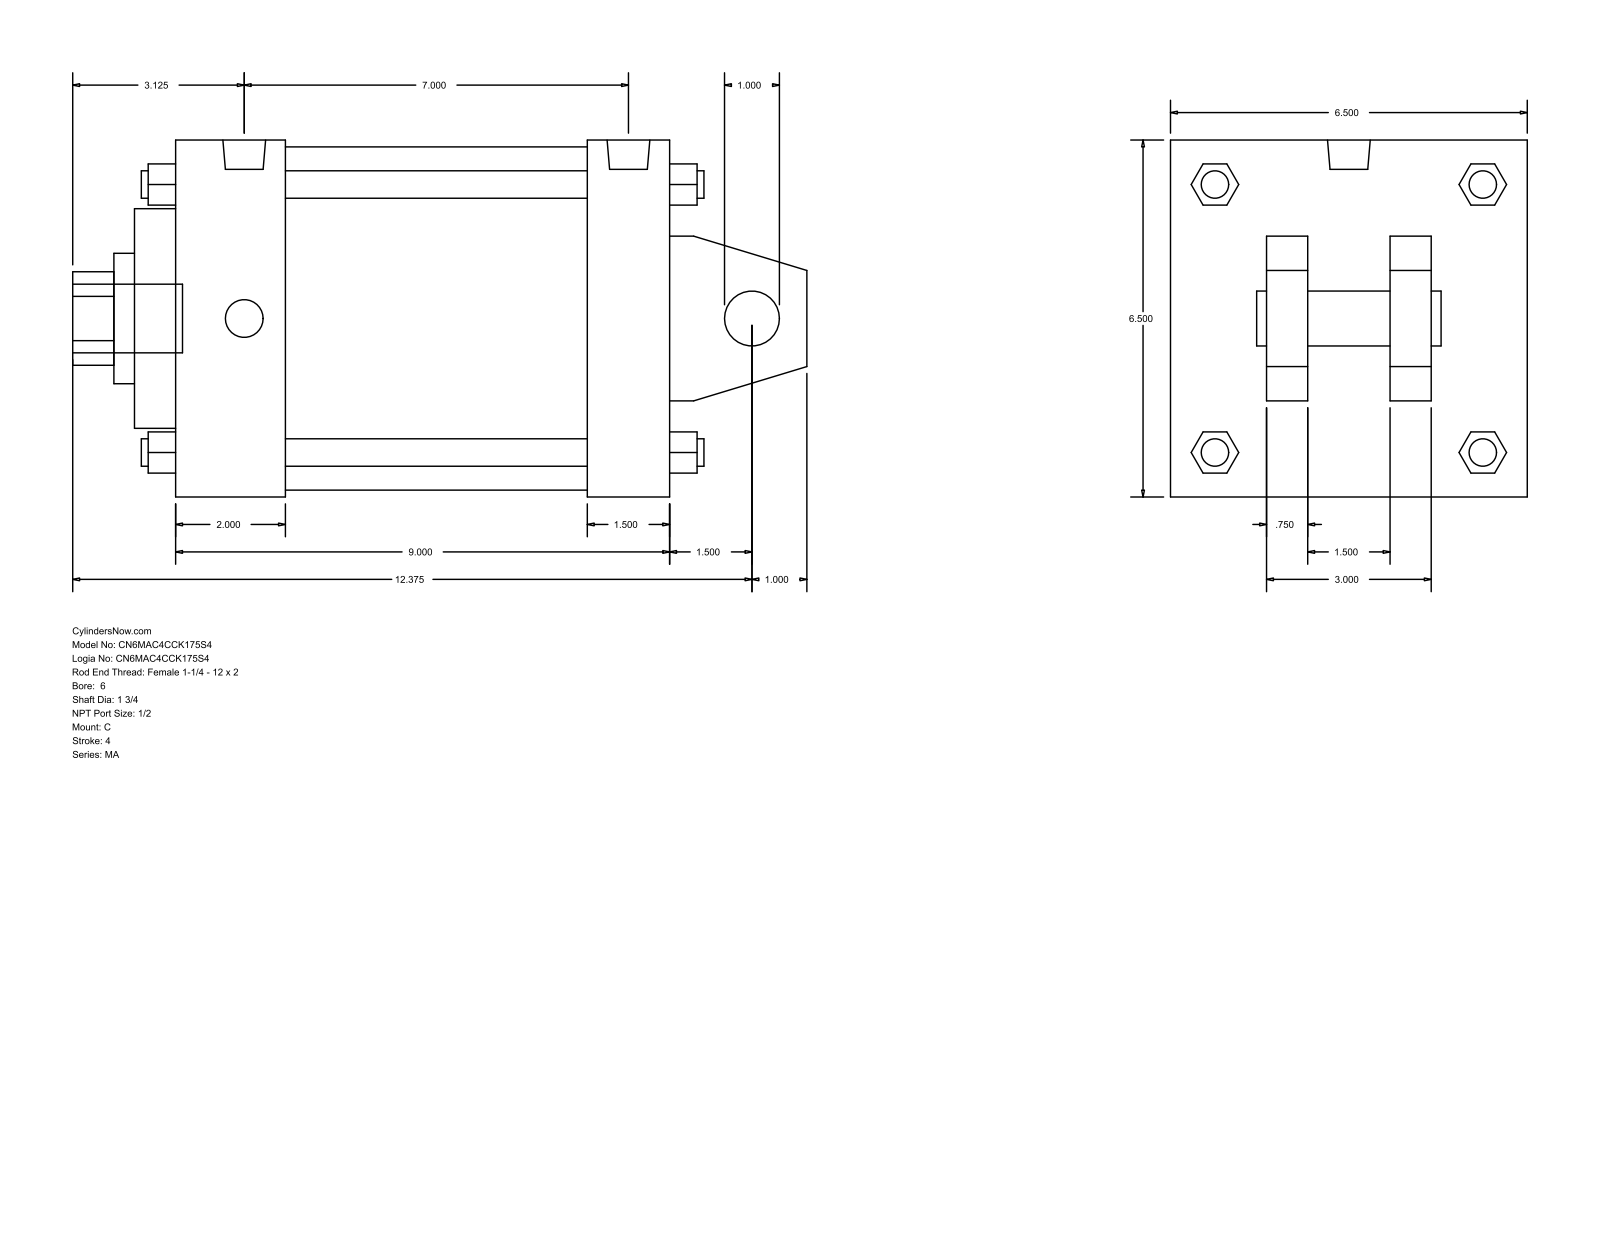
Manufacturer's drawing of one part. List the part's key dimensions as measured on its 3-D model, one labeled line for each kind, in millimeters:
Part name (STEP PRODUCT): MA_C__0600_1.75
STEP written by: GSSL Pune (CONFIG_CONTROL_DESIGN)
Units: millimetres
Bodies: 0 solids, 141 faces (109 planar, 32 cylindrical, 0 other)
Overall size (bounding box): 339.73 × 165.1 × 165.1
Round holes (diameter × count): ⌀25.4 ×1, ⌀44.45 ×1, ⌀60.33 ×1, ⌀101.6 ×1, ⌀158.75 ×1
Round bosses / shafts (diameter × count): ⌀17.46 ×4, ⌀12.7 ×4, ⌀19.77 ×2, ⌀31.75 ×1
Partial cylindrical surfaces — rounded edges, fillets, slot ends (radius × count): R21.63 ×1
Main face-to-face distances: 165.1, 228.61, 19.05, 63.5, 101.6, 50.8, 44.45, 120.65, 57.15, 177.81
